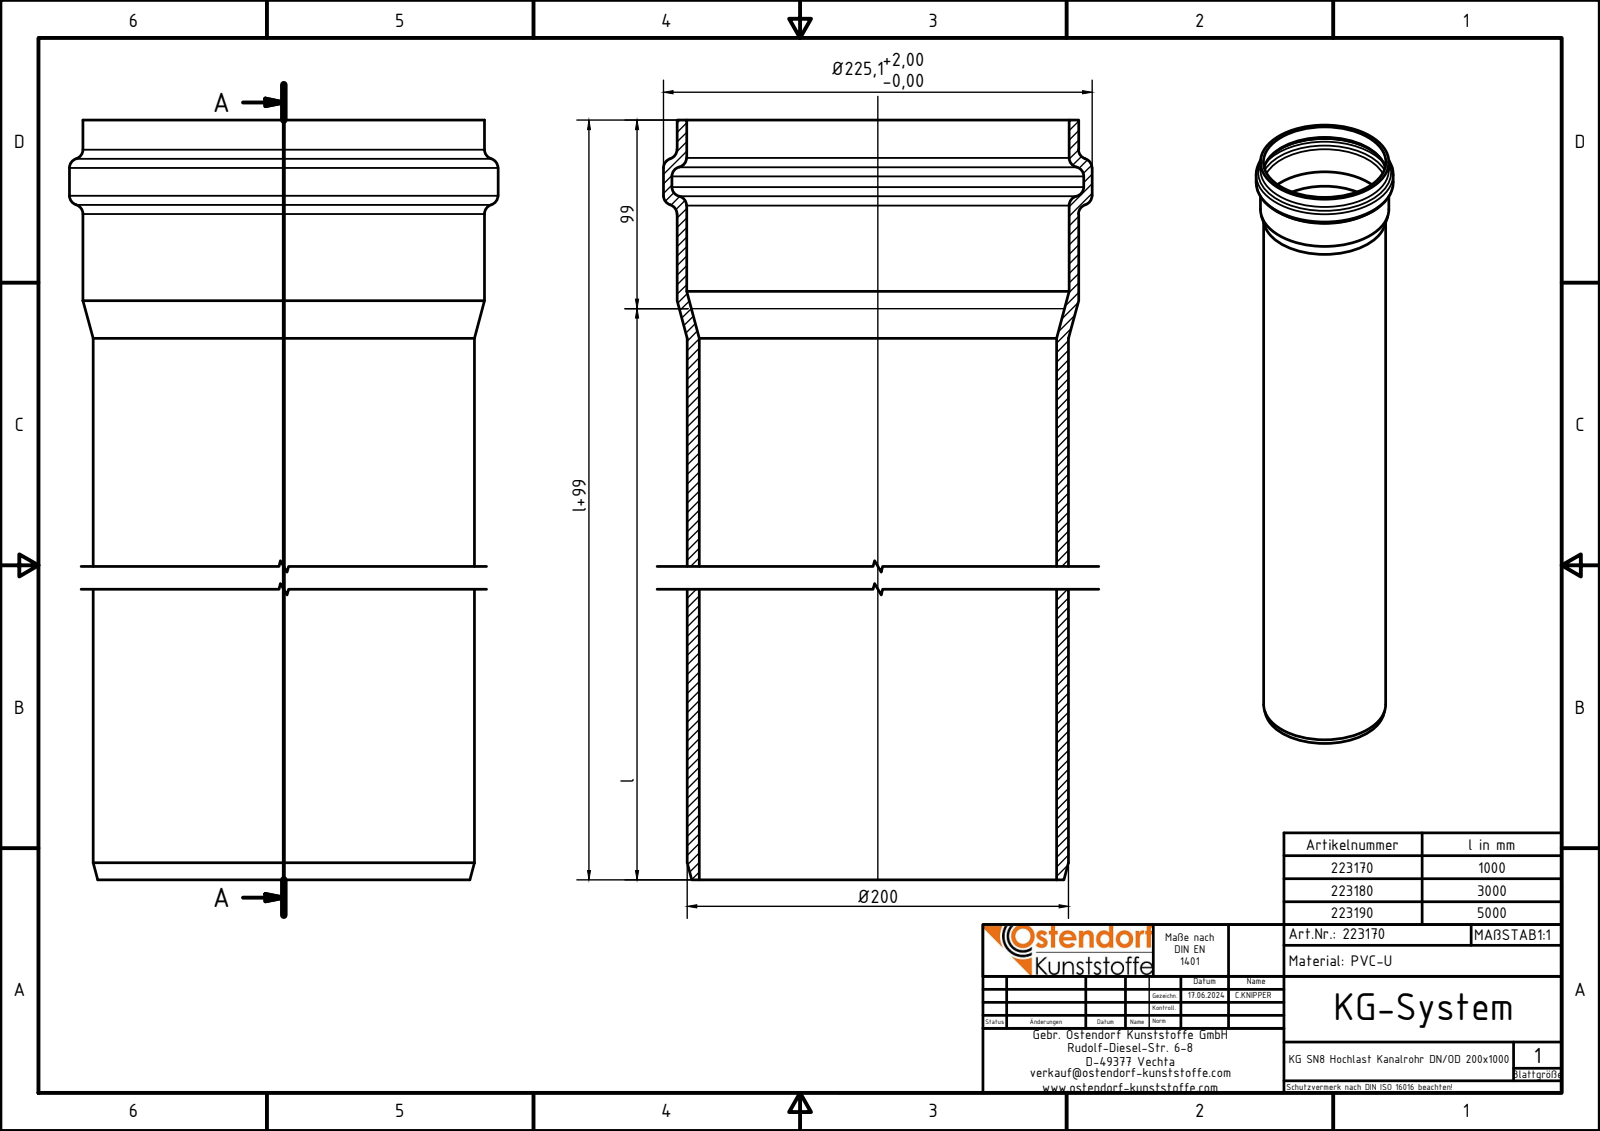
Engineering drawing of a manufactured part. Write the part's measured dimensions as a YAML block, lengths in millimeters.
part_name: "223170 KGEM Passlängen SN 8 DN_OD 200x1000"
step_written_by: "Autodesk Inventor 2016 (AUTOMOTIVE_DESIGN)"
units: millimeters
bodies: {solids: 1, faces: 21, planar: 2, cylindrical: 8, other: 11}
overall_size: [1099, 225.1, 225.1]
volume: 4199000
surface_area: 1365000
round_holes:
  - {diameter: 187.65, count: 1}
  - {diameter: 200.85, count: 1}
  - {diameter: 216.3, count: 1}
round_bosses_or_shafts:
  - {diameter: 225.1, count: 1}
  - {diameter: 210.85, count: 1}
  - {diameter: 200.25, count: 1}
face_to_face_distances: [1099]
